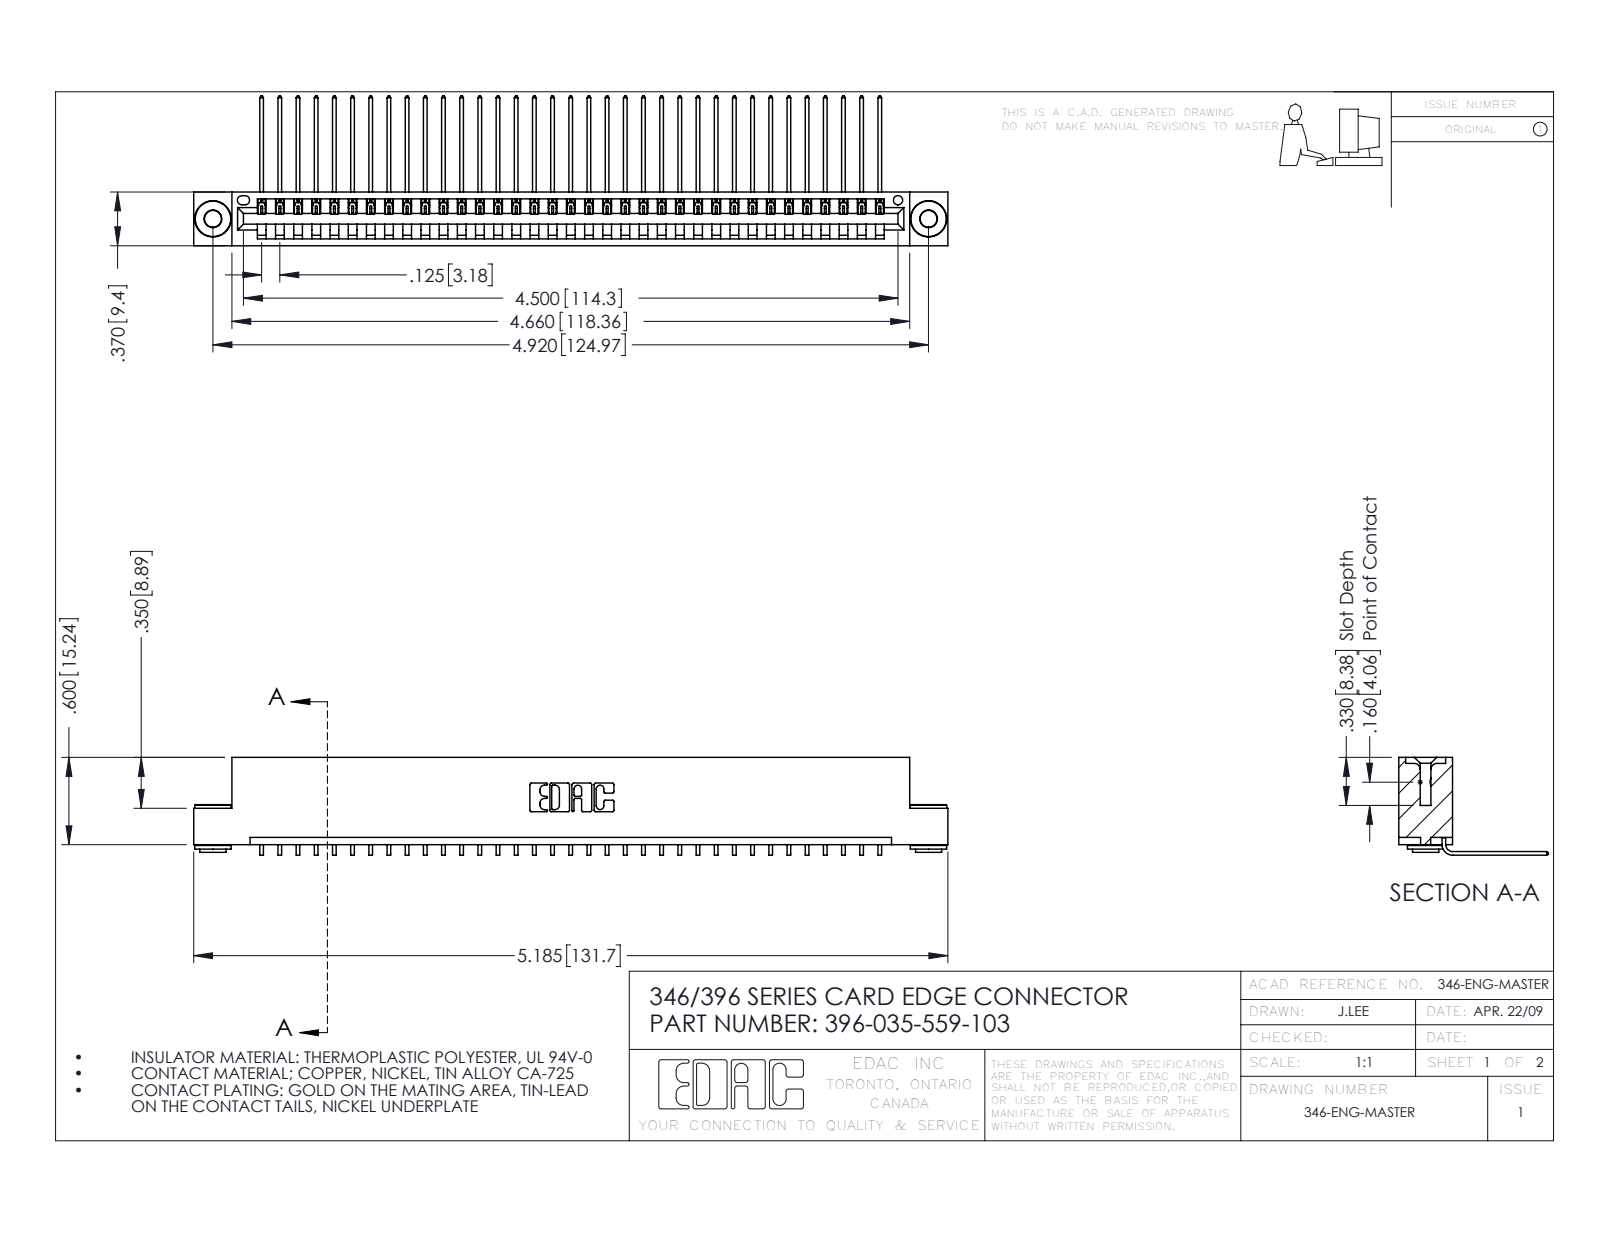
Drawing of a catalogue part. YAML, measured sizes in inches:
part_name: "345-292-001_558 559 Tail - 1; 346 Part_Flush Mounting Lugs - 0.156 Dia-TH; 396-035-559-103; 345-250-002_345-250-002-102"
step_written_by: "SolidWorks 2016 (CONFIG_CONTROL_DESIGN)"
units: inches
bodies: {solids: 38, faces: 2260, planar: 1556, cylindrical: 696, other: 8}
overall_size: [5.185, 1.03, 0.673]
volume: 0.775
surface_area: 25.89
round_holes:
  - {diameter: 0.116, count: 2}
  - {diameter: 0.156, count: 2}
  - {diameter: 0.064, count: 1}
round_bosses_or_shafts:
  - {diameter: 0.25, count: 2}
  - {diameter: 0.18, count: 2}
  - {diameter: 0.136, count: 2}
partial_cylinders:
  - {radius: 0.006, count: 70}
  - {radius: 0.01, count: 22}
  - {radius: 0.007, count: 6}
  - {radius: 0.031, count: 6}
  - {radius: 0.026, count: 3}
  - {radius: 0.031, count: 2}
  - {radius: 0.04, count: 2}
  - {radius: 0.014, count: 1}
face_to_face_distances: [0.048, 0.322, 0.37, 0.25, 0.025, 0.072, 0.298, 0.148, 0.222, 0.1]
hole_center_spacings: [0.246, 4.711, 4.92]
